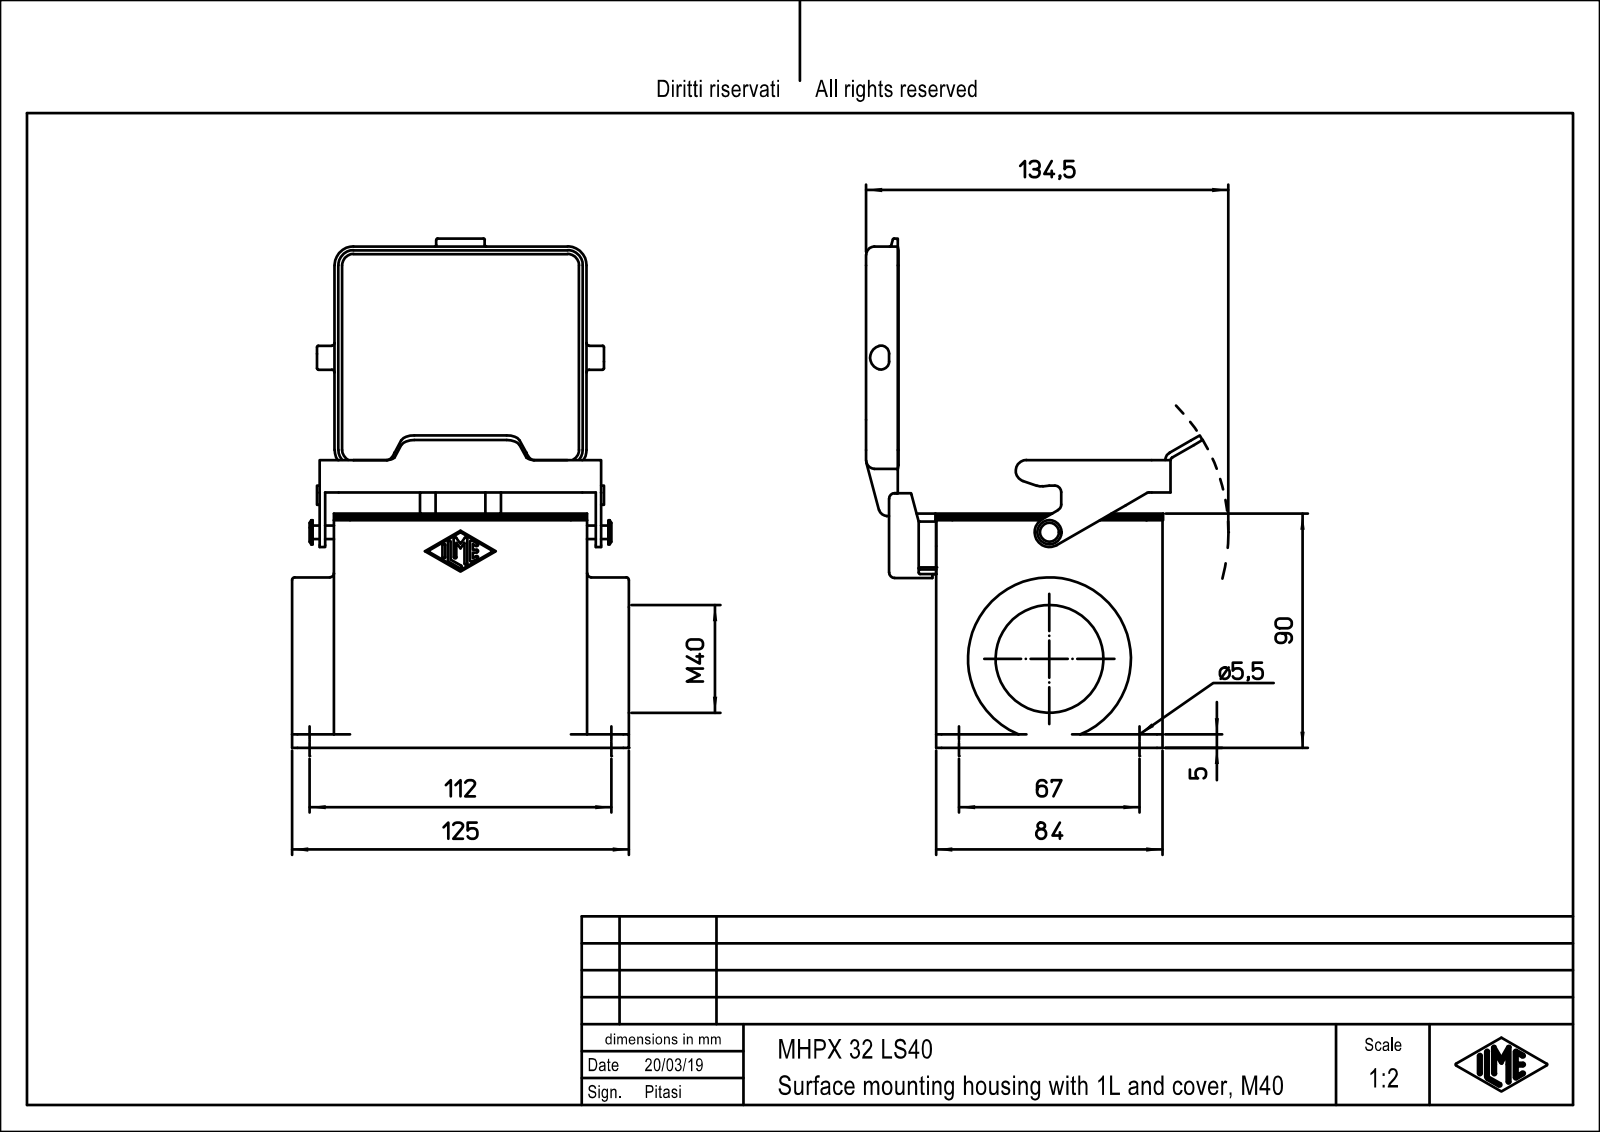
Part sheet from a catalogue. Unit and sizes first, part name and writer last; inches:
Units: inches
Overall size (bounding box): 7.441 × 4.921 × 4.916
Round holes (diameter × count): ⌀0.118 ×8, ⌀0.217 ×4, ⌀0.165 ×1, ⌀1.181 ×1, ⌀1.575 ×1
Round bosses / shafts (diameter × count): ⌀2.382 ×1, ⌀0.354 ×1, ⌀0.236 ×1, ⌀0.197 ×1
Partial cylindrical surfaces — rounded edges, fillets, slot ends (radius × count): R0.118 ×14, R0.079 ×11, R0.059 ×9, R0.236 ×8, R0.02 ×6, R0.276 ×6, R0.197 ×5, R0.165 ×4
Main face-to-face distances: 0.118, 3.189, 0.079, 1.063, 0.157, 3.307, 4.252, 4.331, 0.945, 1.024
Hole centre spacings: 0.684, 1.063, 1.328, 1.417, 1.643, 2.648, 3.051, 3.231
Volume: 17.3 in³ · Surface area: 198.5 in²
Bodies: 1 solid, 337 faces (178 planar, 139 cylindrical, 20 other)
Part name (STEP PRODUCT): CHPX_32_L; MHPX_32_LS40; MHPX_32_LS40.stp
STEP written by: PTC Creo Elements/Direct Modeling 19.0E 27-Jun-2016 (C) Parametric Technology GmbH (AUTOMOTIVE_DESIGN)
